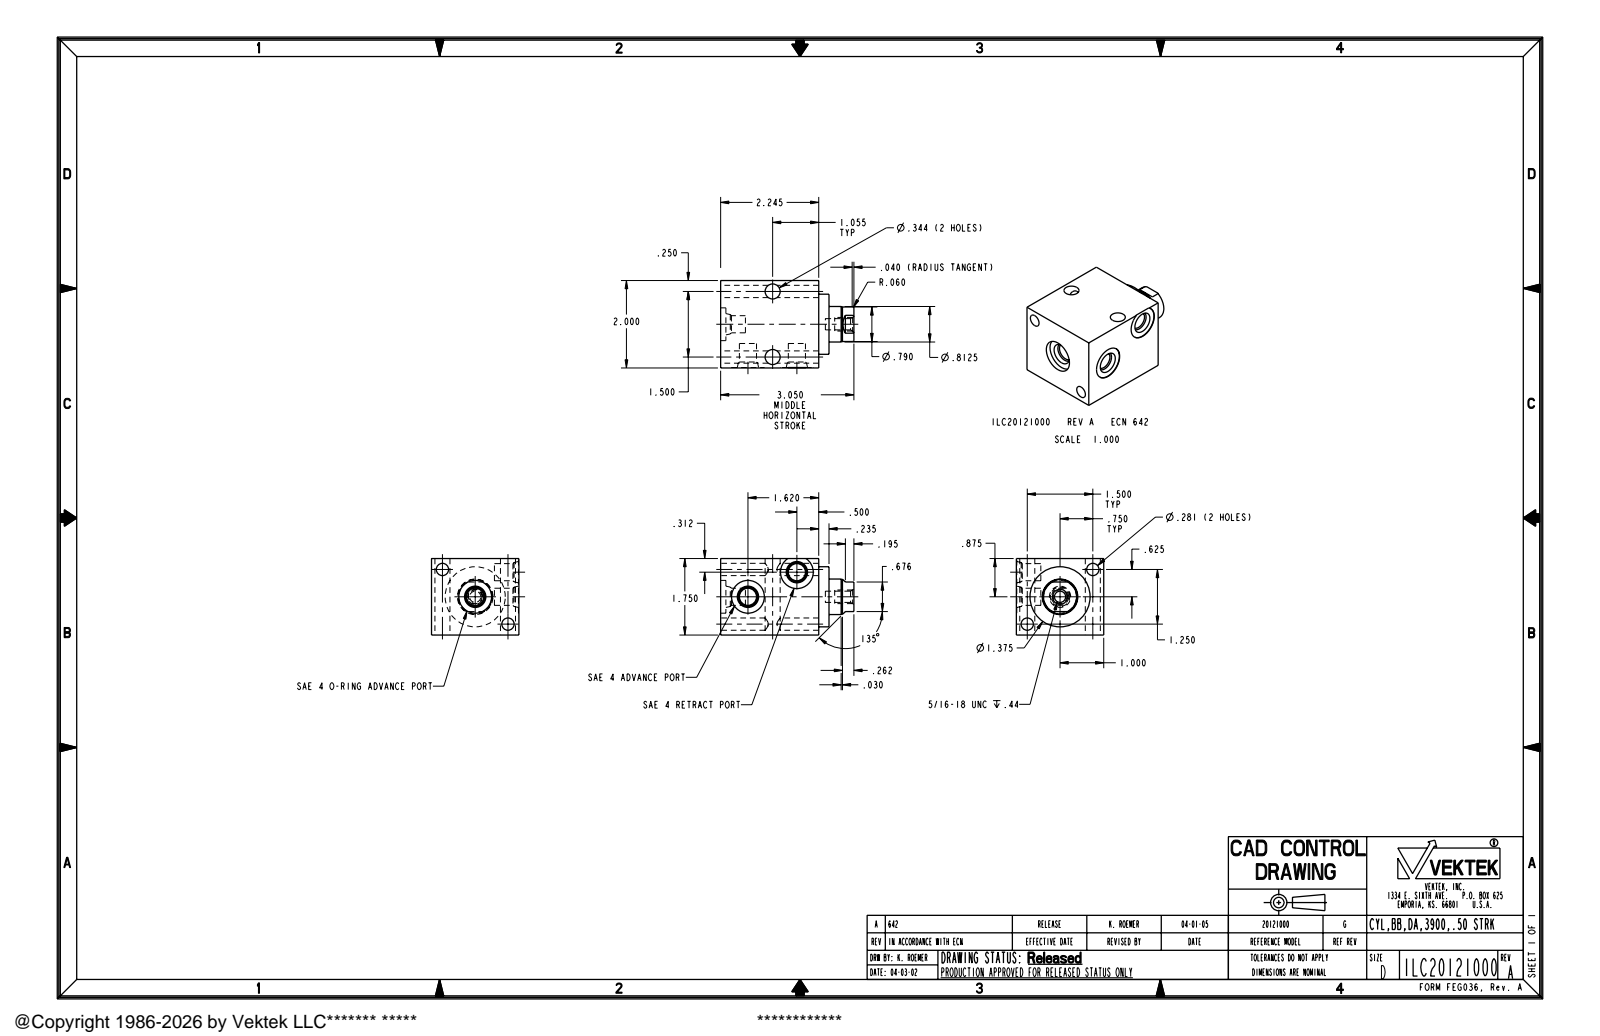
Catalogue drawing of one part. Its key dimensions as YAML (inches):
part_name: "ILC20121000"
step_written_by: "PRO/ENGINEER BY PARAMETRIC TECHNOLOGY CORPORATION, 2004290 (AUTOMOTIVE_DESIGN_CC2)"
units: inches
bodies: {solids: 1, faces: 71, planar: 20, cylindrical: 33, other: 18}
overall_size: [3.05, 2, 1.75]
volume: 7.622
surface_area: 35.67
round_holes:
  - {diameter: 0.392, count: 3}
  - {diameter: 0.75, count: 3}
  - {diameter: 0.281, count: 2}
  - {diameter: 0.344, count: 2}
  - {diameter: 0.257, count: 1}
round_bosses_or_shafts:
  - {diameter: 1.375, count: 1}
  - {diameter: 0.813, count: 1}
  - {diameter: 0.79, count: 1}
  - {diameter: 0.312, count: 1}
face_to_face_distances: [1.75, 2, 2.245, 0.235, 2.48, 1.99, 0.57, 0.805, 3.05, 2.93]
hole_center_spacings: [0.976, 1.254, 1.5, 1.953]
